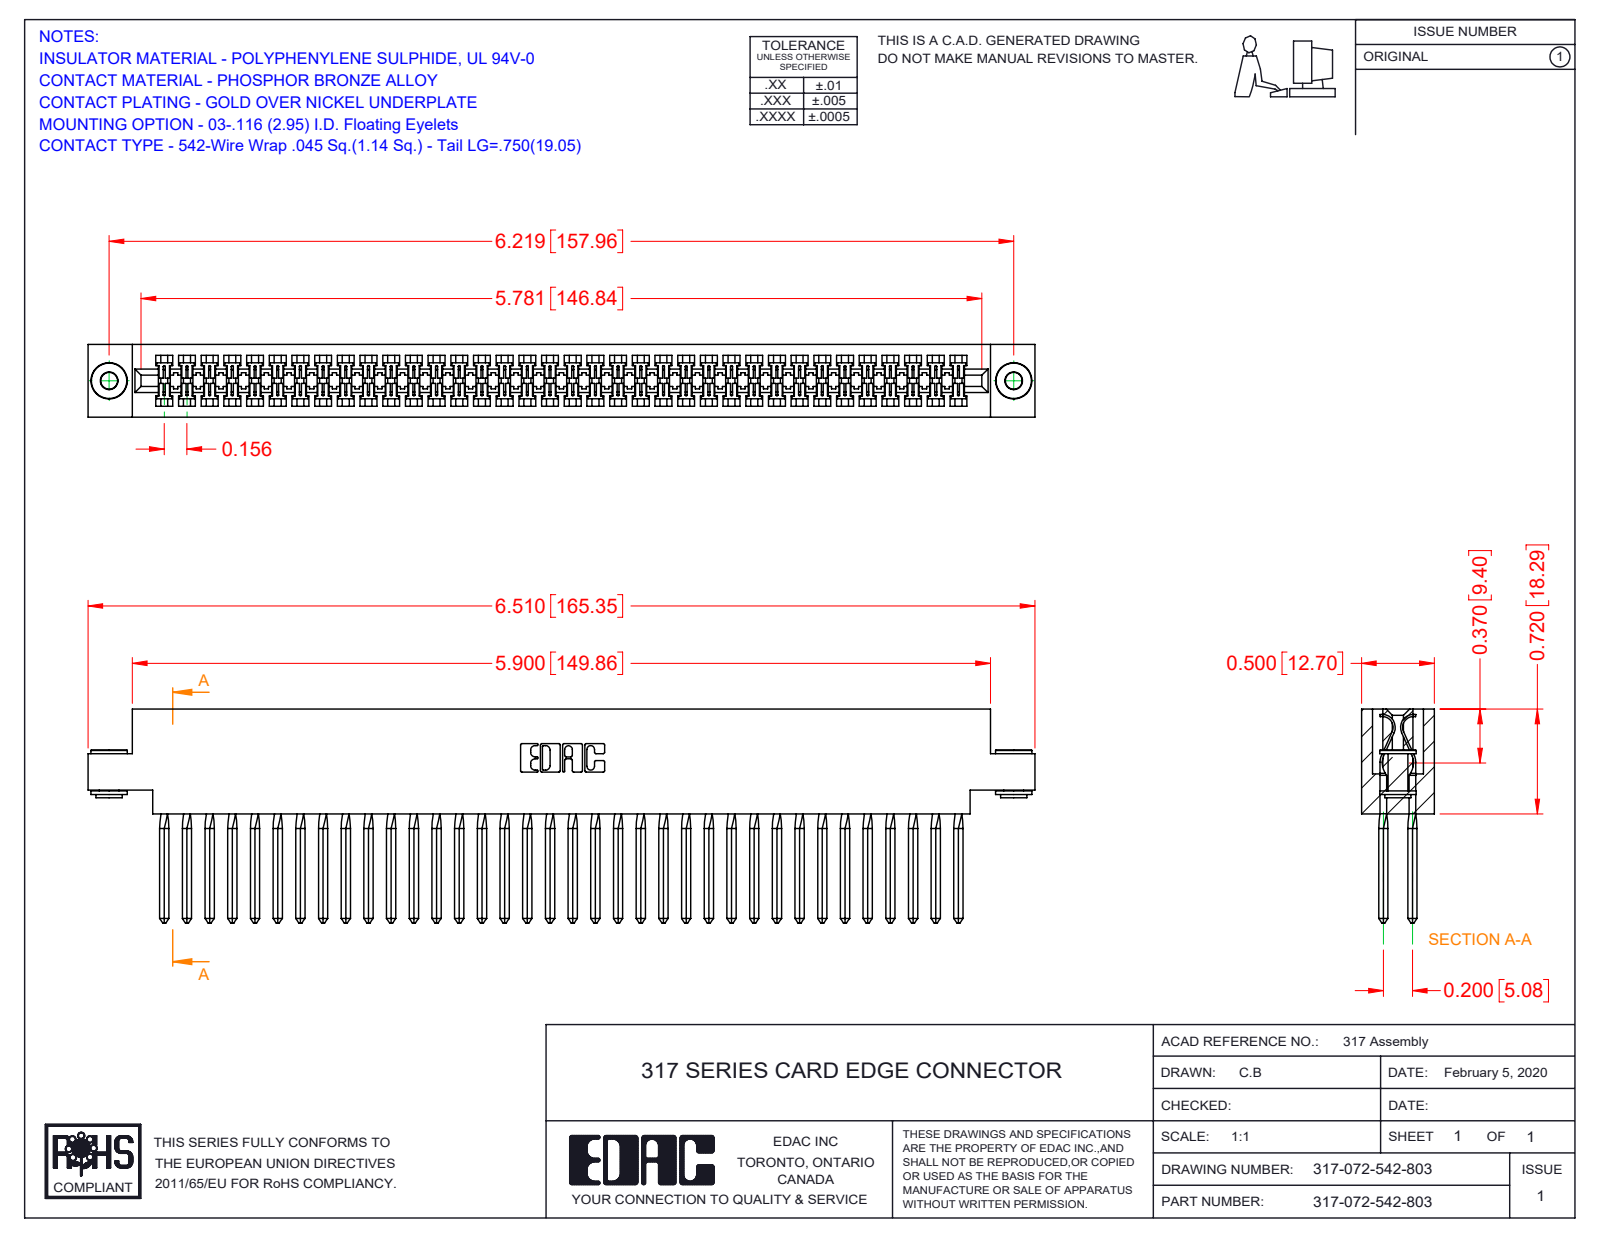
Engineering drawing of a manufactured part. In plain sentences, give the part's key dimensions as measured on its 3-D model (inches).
The part is named "345-250-002_345-250-002-102; 317-290-003_542; 317 Part_.156 Dia - TH; 317-072-542-803". Its 3-D file was written by "SolidWorks 2016 (CONFIG_CONTROL_DESIGN)". It is 75 solids with 4244 faces: 3380 planar, 568 cylindrical and 296 other. Overall it measures 6.51 by 1.47 by 0.5 inches. Its volume is 1.642 cubic inches and its surface area 58.03 square inches. Round holes: 2 of diameter 0.116, 2 of diameter 0.156. Round bosses or shafts: 2 of diameter 0.25, 2 of diameter 0.18, 2 of diameter 0.136. Partial cylindrical surfaces (rounded edges, fillets, slot ends): 144 of radius 0.006, 22 of radius 0.01, 6 of radius 0.007, 6 of radius 0.031, 3 of radius 0.026, 2 of radius 0.074, 2 of radius 0.089, 2 of radius 0.1. The main face-to-face distances are 0.5, 0.075, 0.425, 0.35, 0.2, 0.046, 0.128, 0.372, 0.052, 0.297. The hole center spacings are 6.219.
